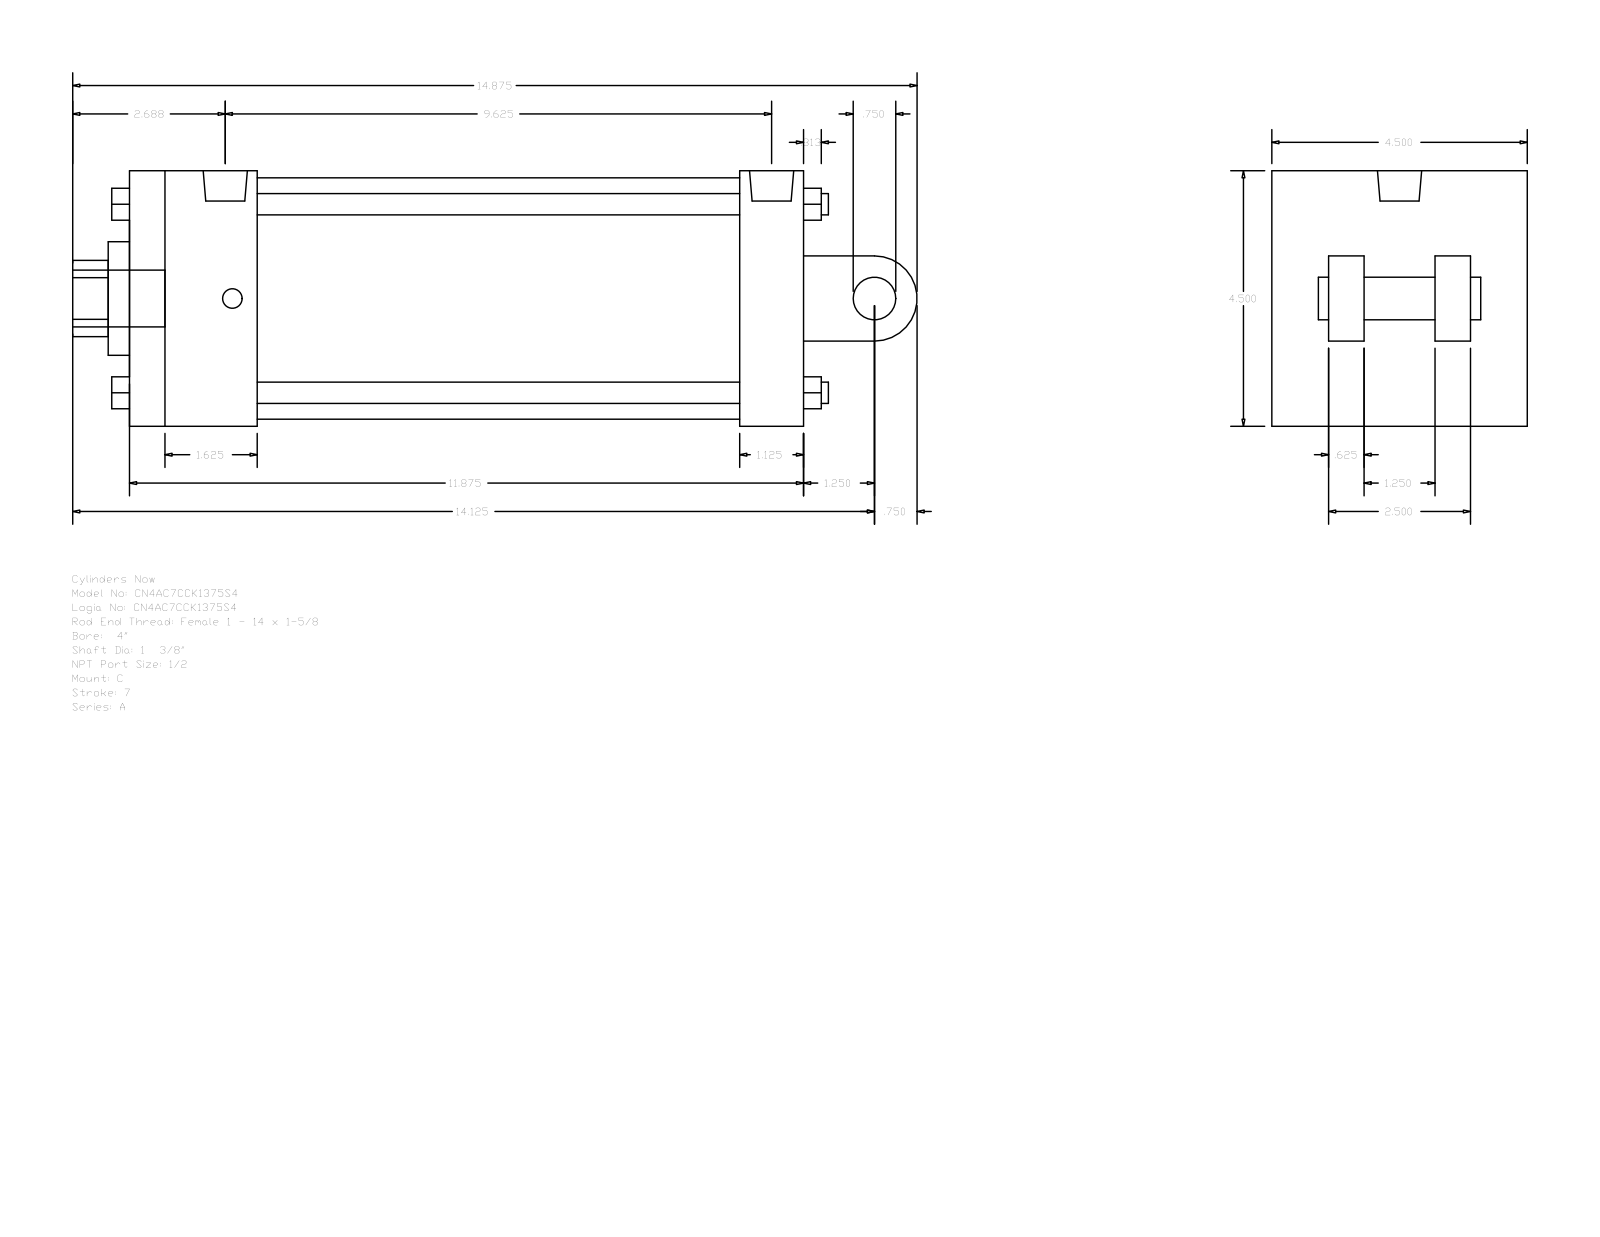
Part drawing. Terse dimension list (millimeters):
name: A_C__0400_1.375
written by: GSSL Pune (CONFIG_CONTROL_DESIGN)
unit: mm
bodies: 0 solids, 135 faces (102 planar, 33 cylindrical, 0 other)
size: 377.82 × 114.3 × 114.3
holes: 2× ⌀8.73, 1× ⌀19.77, 1× ⌀34.92, 1× ⌀50.8, 1× ⌀107.95
bosses: 4× ⌀9.53, 2× ⌀8.73, 1× ⌀25.4, 1× ⌀19.77, 1× ⌀19.05
rounds: 1× R17.06, 1× R19.05
face distances: 114.3, 301.62, 73.03, 28.57, 273.05, 57.15, 215.9, 244.47, 15.87, 41.27
hole spacings: 3.18
